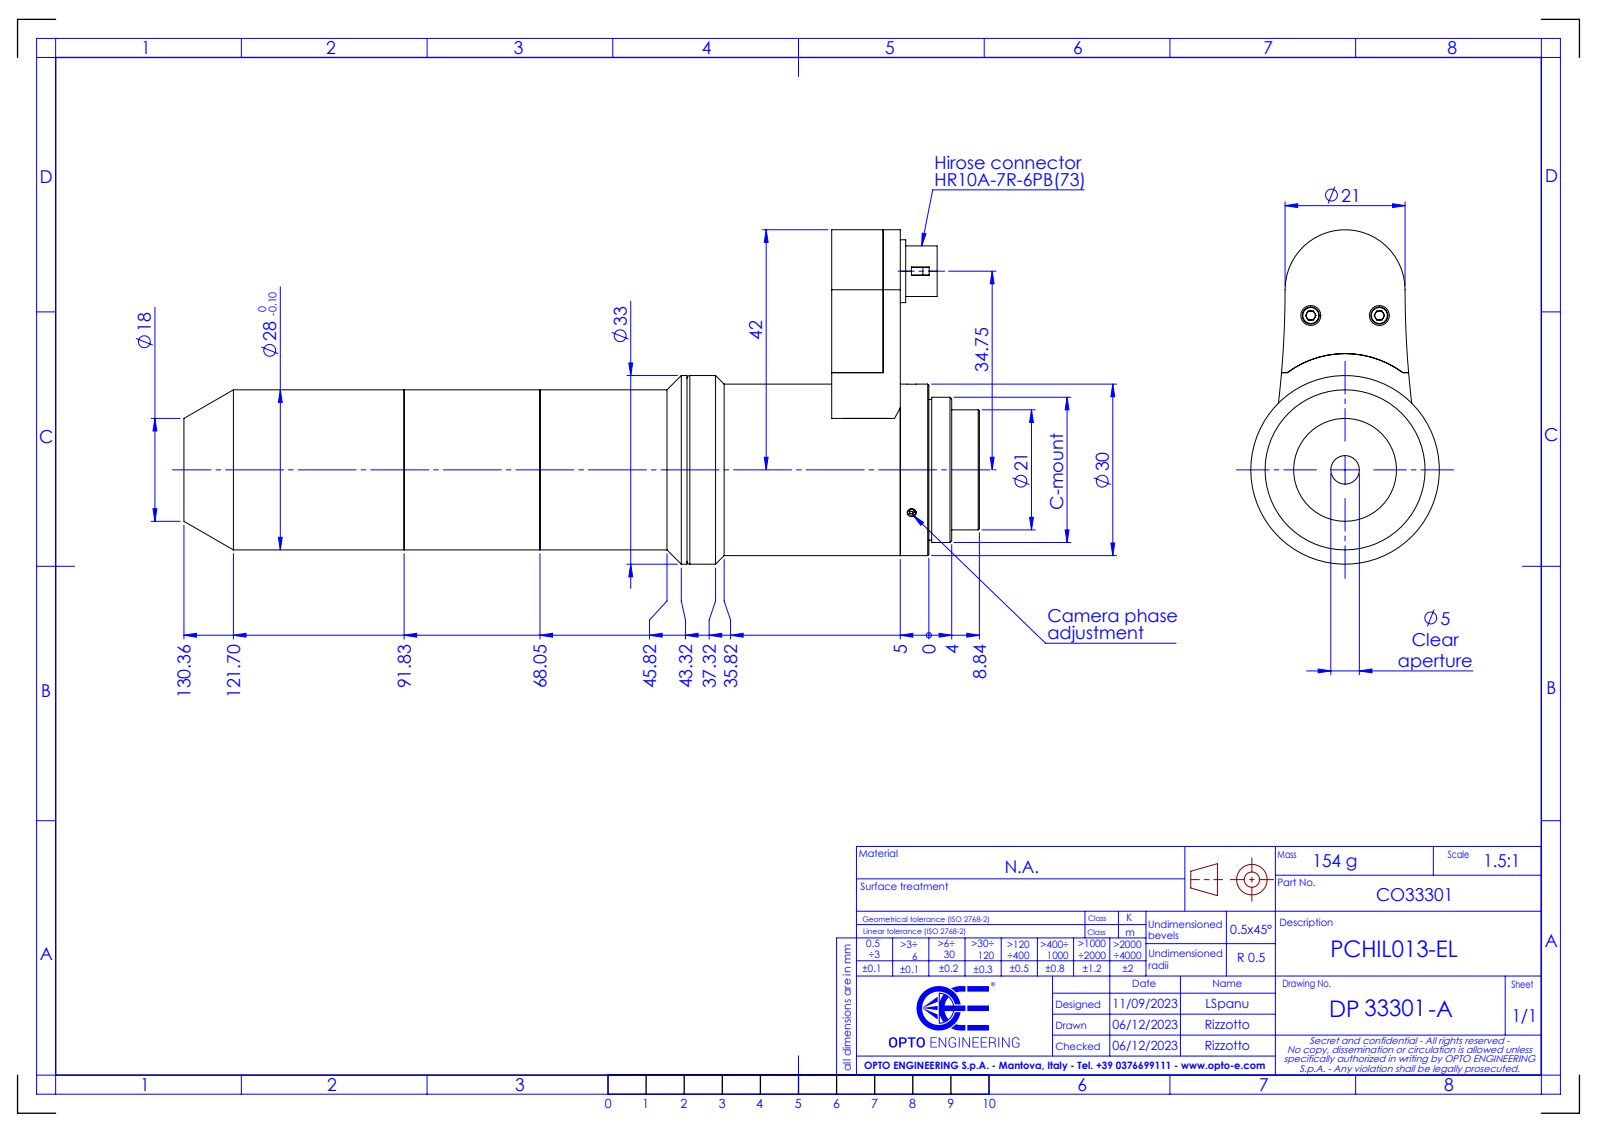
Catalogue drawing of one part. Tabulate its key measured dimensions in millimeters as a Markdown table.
| quantity | value |
| --- | --- |
| part name | DP33301-A_PCHIL013-EL |
| STEP written by | SolidWorks 2021 (CONFIG_CONTROL_DESIGN) |
| units | millimeters |
| bodies | 0 solids, 199 faces (76 planar, 81 cylindrical, 42 other) |
| overall size | 139.2 × 58.5 × 33 |
| round holes (diameter × count) | 1.6 × 3, 1.5 × 2, 3.5 × 2, 5 × 1, 7.4 × 1, 10.5 × 1 |
| round bosses / shafts (diameter × count) | 1.2 × 2, 33 × 1, 30 × 1, 28 × 1, 25.4 × 1, 24.6 × 1, 23 × 1, 21 × 1 |
| partial cylindrical surfaces (radius × count) | 169.5 × 2, 3.6 × 1, 3.9 × 1, 4 × 1, 10.5 × 1, 17 × 1 |
| main face-to-face distances | 12, 113.36, 125.36, 139.2, 25.84, 13.84, 130.36, 17, 5, 8.84 |
| hole center spacings | 7.9, 9.8, 20.02, 27.66, 35.41, 12, 15.8, 26.85 |
